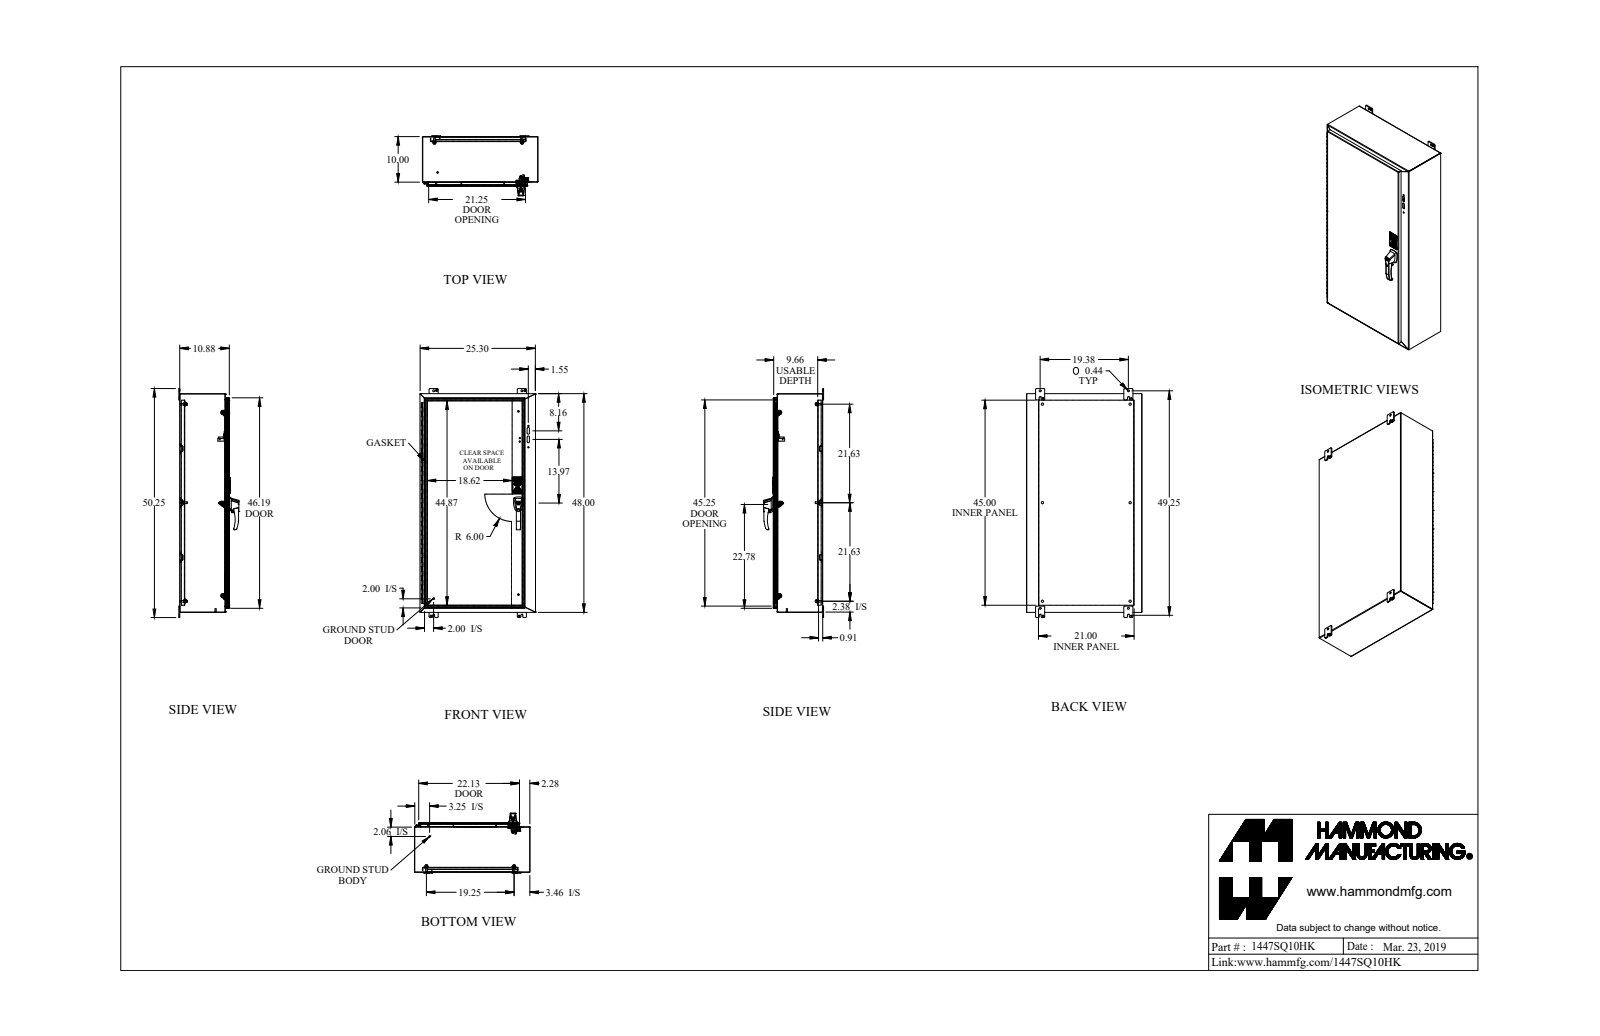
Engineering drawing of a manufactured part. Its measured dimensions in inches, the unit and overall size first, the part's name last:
Units: inches
Overall size (bounding box): 50.25 × 25.375 × 13.177
Round holes (diameter × count): ⌀0.176 ×6, ⌀0.313 ×6, ⌀0.5 ×6, ⌀0.307 ×4, ⌀0.437 ×4, ⌀0.445 ×4, ⌀0.25 ×3, ⌀0.265 ×3, ⌀0.413 ×3, ⌀0.156 ×2, ⌀0.173 ×2, ⌀0.196 ×2
Round bosses / shafts (diameter × count): ⌀0.375 ×11, ⌀0.25 ×9, ⌀1 ×7, ⌀0.65 ×6, ⌀0.33 ×6, ⌀0.156 ×6, ⌀0.63 ×2, ⌀0.51 ×2
Partial cylindrical surfaces — rounded edges, fillets, slot ends (radius × count): R0.188 ×32, R0.25 ×25, R0.036 ×18, R0.108 ×18, R0.125 ×14, R0.116 ×12, R0.03 ×8, R0.218 ×8
Main face-to-face distances: 0.072, 10.803, 10.731, 10.875, 0.095, 25.303, 9.771, 9.699, 1.032, 1.104
Hole centre spacings: 1.735, 19.375, 47.75, 51.531, 1.11, 19.25, 18.835, 20.05
Volume: 448.7 in³ · Surface area: 11 462 in²
Bodies: 68 solids, 1968 faces (994 planar, 788 cylindrical, 186 other)
Part name (STEP PRODUCT): 1447SQ10HK_Default
STEP written by: SolidWorks 2019 (CONFIG_CONTROL_DESIGN)
